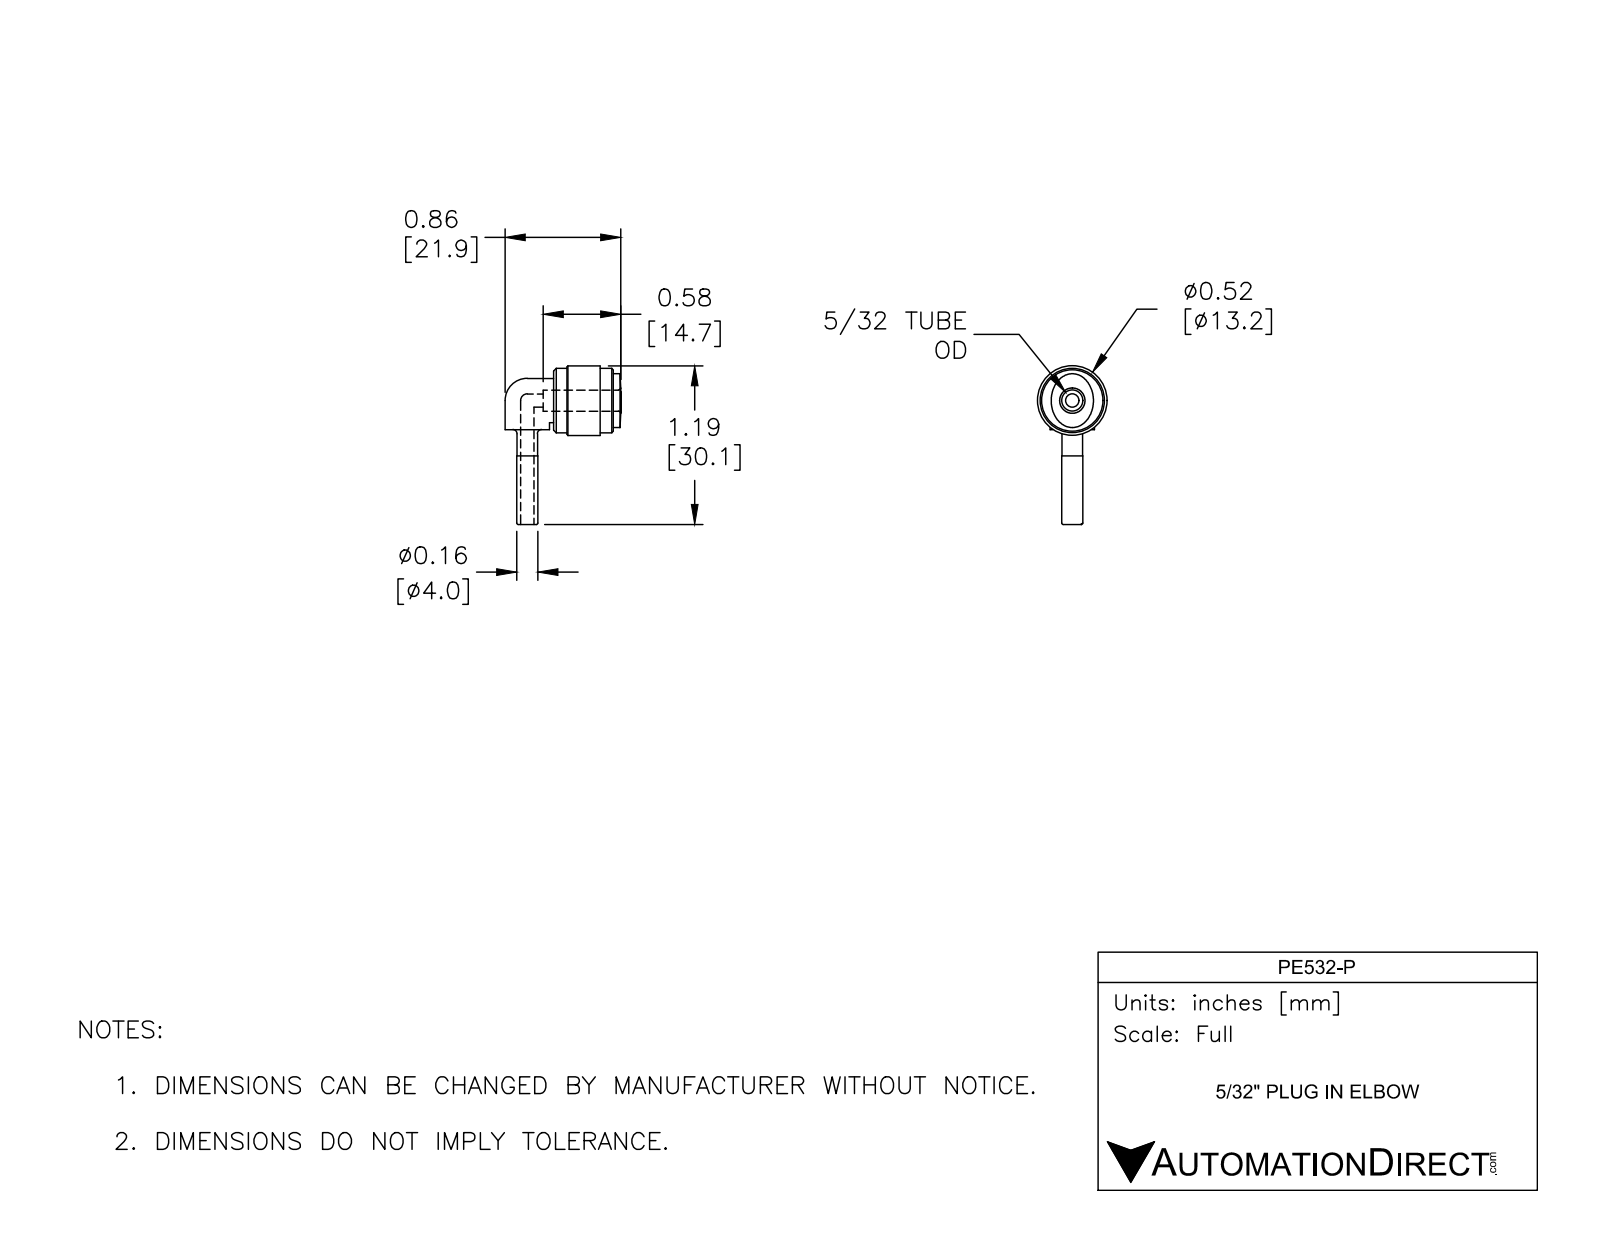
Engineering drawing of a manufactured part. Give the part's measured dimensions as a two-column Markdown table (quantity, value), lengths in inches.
| quantity | value |
| --- | --- |
| part name | PE532-P |
| STEP written by | SolidWorks 2017 (AUTOMOTIVE_DESIGN) |
| units | inches |
| bodies | 1 solid, 48 faces (8 planar, 20 cylindrical, 20 other) |
| overall size | 1.185 × 0.862 × 0.52 |
| volume | 0.122 in³ |
| surface area | 2.482 in² |
| round holes (diameter × count) | 0.098 × 2, 0.157 × 1 |
| round bosses / shafts (diameter × count) | 0.331 × 2, 0.52 × 1, 0.48 × 1, 0.157 × 1, 0.154 × 1 |
| main face-to-face distances | 0.445, 0.098, 0.346, 0.248, 0.079, 0.177, 0.425, 0.524, 0.709, 0.512 |
